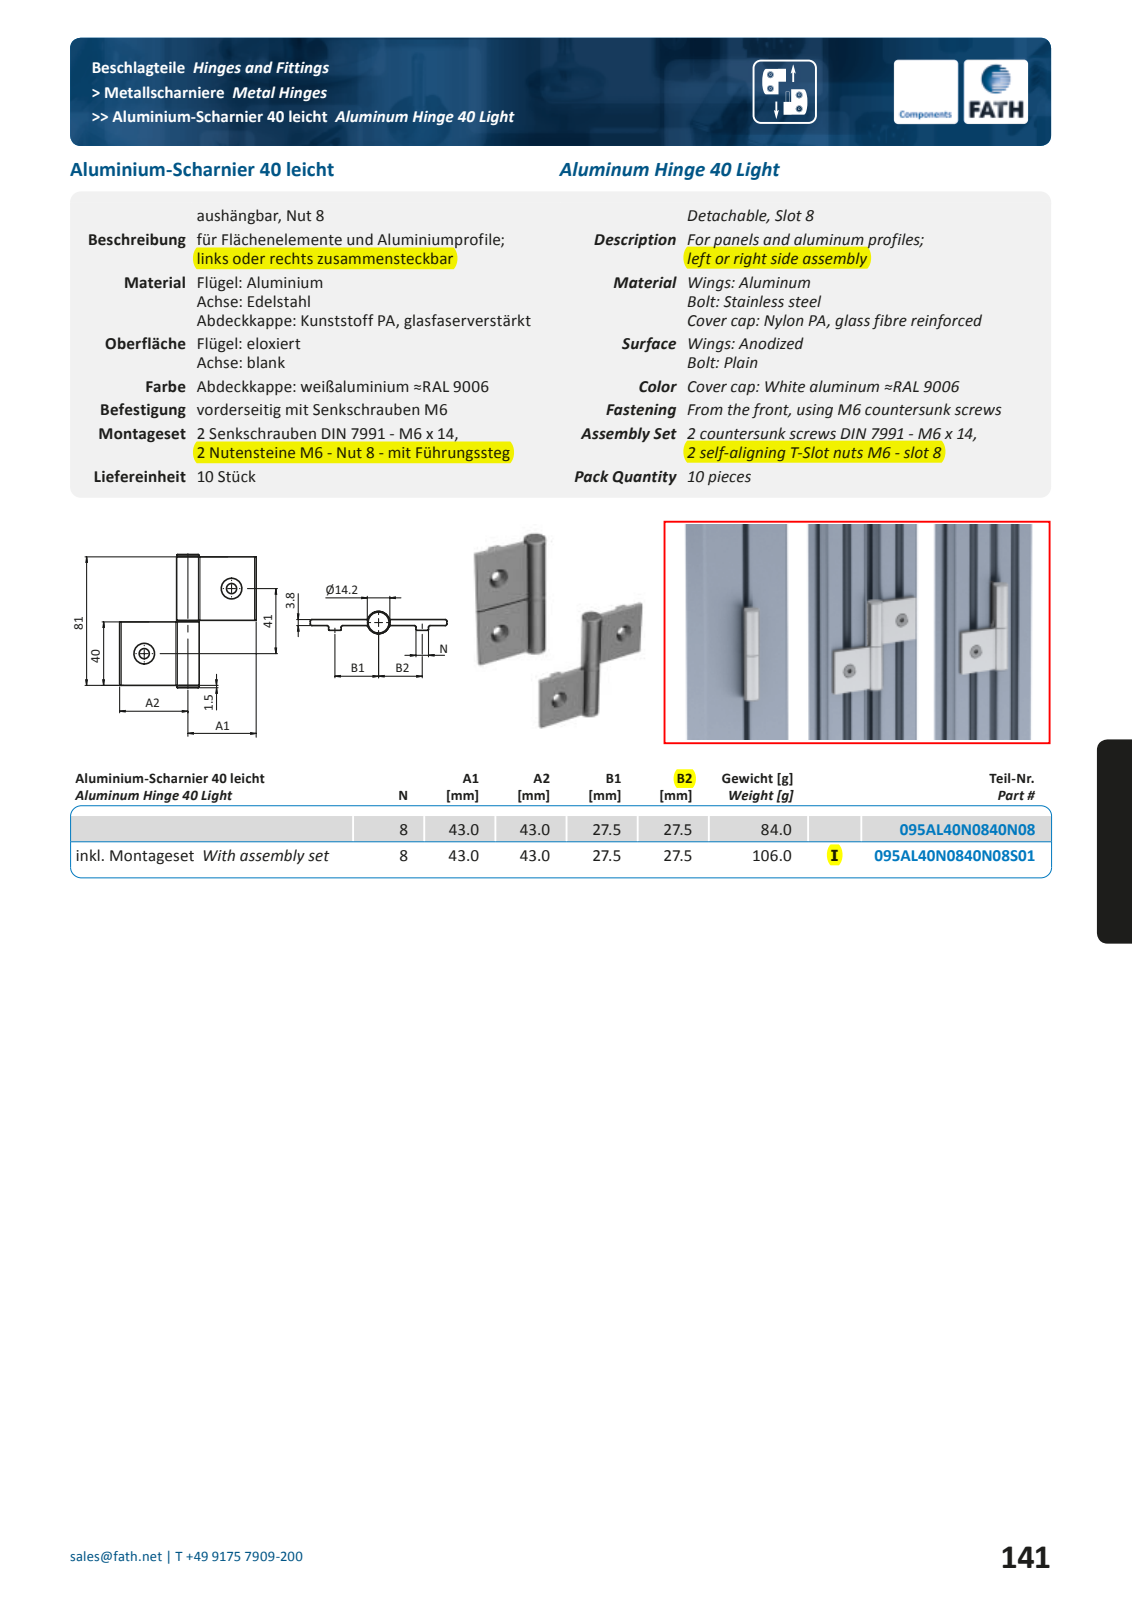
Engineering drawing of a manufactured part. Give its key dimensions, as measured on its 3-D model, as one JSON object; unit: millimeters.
{"part_name": "fath_095al40n0840n08s01_1; fath_095al40n0840n08s01_2; fath_095al40n0840n08s01_3; fath_095al40n0840n08s01_4 (+8 more)", "step_written_by": "Spatial InterOp 3D (automotive_design)", "units": "millimeters", "bodies": {"solids": 17, "faces": 548, "planar": 146, "cylindrical": 174, "other": 228}, "overall_size": [350.19, 87.17, 86], "volume_mm3": 28367, "surface_area_mm2": 22745, "round_holes": [[5, 4], [6.4, 2], [4.2, 1], [6, 1], [12, 1]], "round_bosses_or_shafts": [[11.57, 2], [6, 2], [14.2, 1], [14, 1], [13.9, 1], [8, 1], [5.9, 1]], "partial_cylinders_radius": [[1, 12], [0.2, 8], [0.5, 8], [15, 4]], "face_to_face_distances": [3.8, 40, 270.41, 3, 6.8, 12.22, 310.41, 230.41, 0.8, 0.85], "hole_center_spacings": [10.5, 276.46, 0.78, 10.76, 11.28, 265.41, 266.17, 275.69]}
